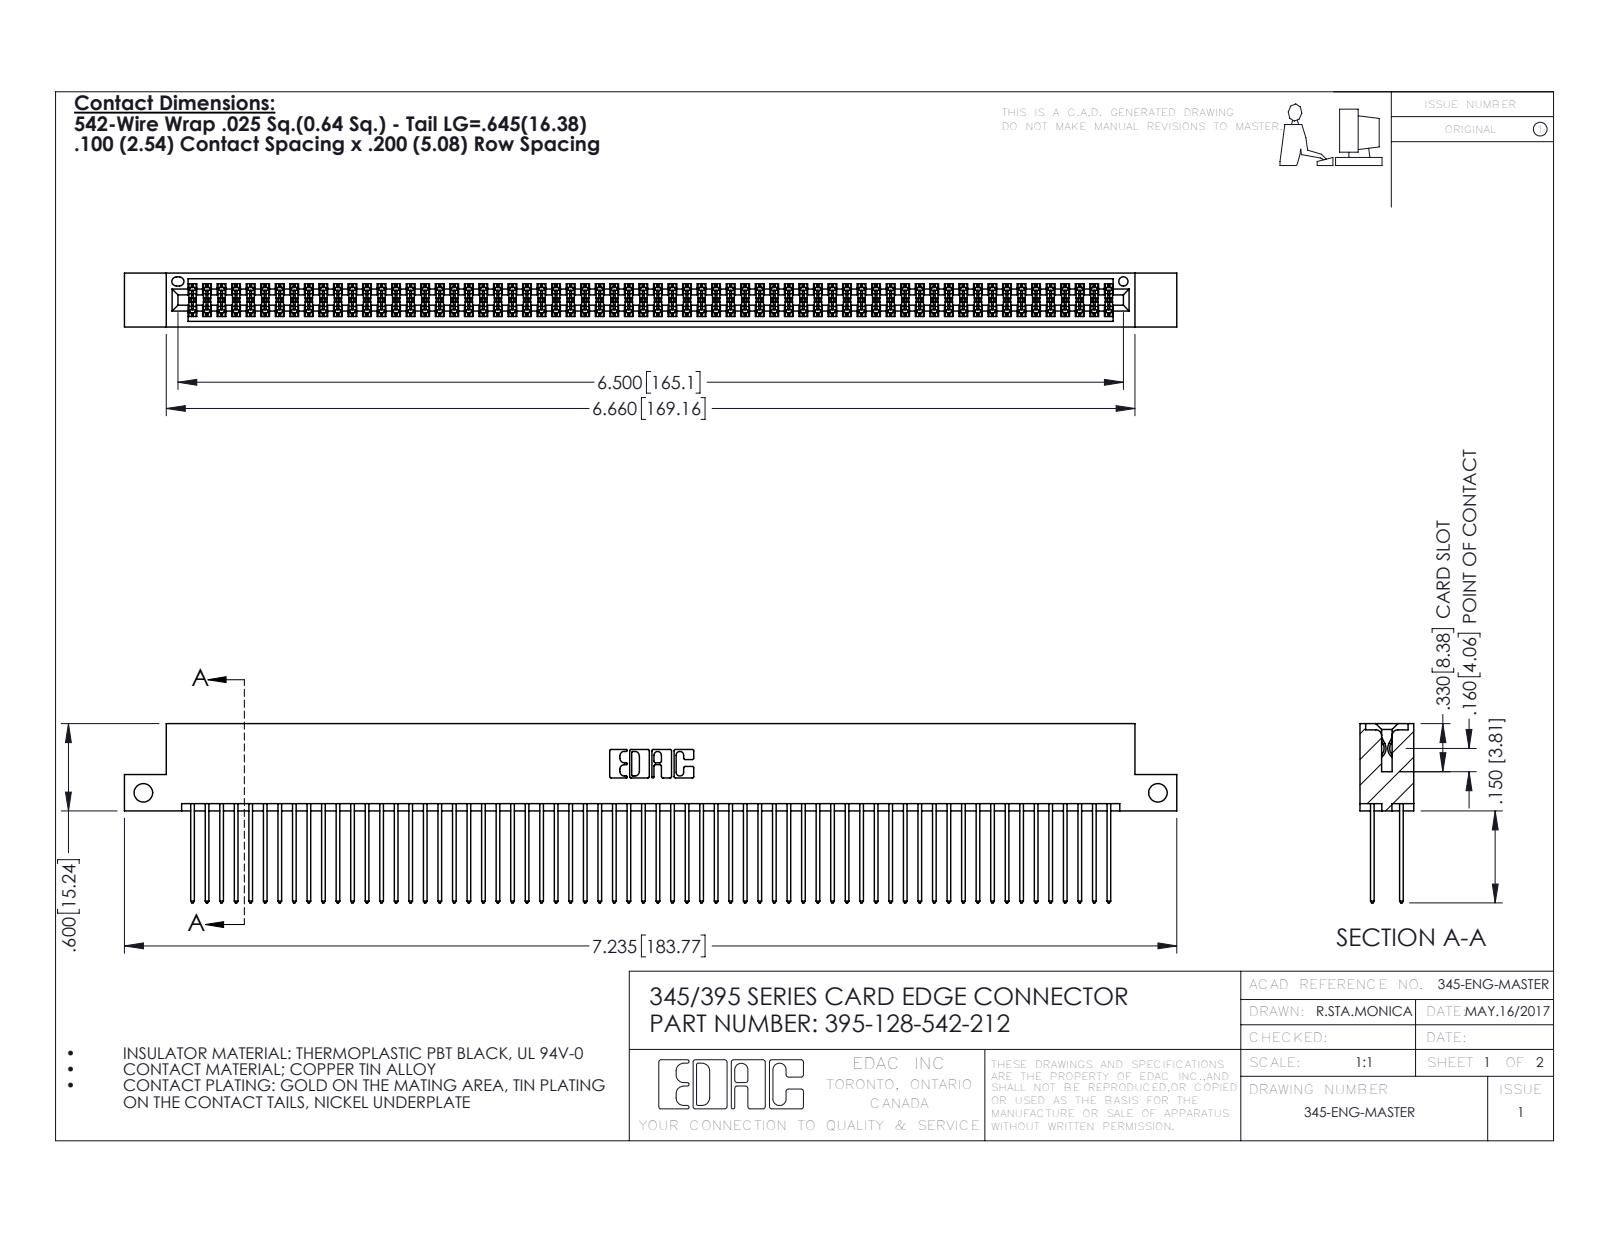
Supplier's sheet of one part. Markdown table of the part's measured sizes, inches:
| quantity | value |
| --- | --- |
| part name | 395-128-542-212; 345-292-001_345-293-142; 345 Part_Flush Mounting Lugs - Side Mount |
| STEP written by | SolidWorks 2016 (CONFIG_CONTROL_DESIGN) |
| units | inches |
| bodies | 129 solids, 6526 faces (4304 planar, 2222 cylindrical, 0 other) |
| overall size | 7.235 × 1.232 × 0.37 |
| volume | 1.133 in³ |
| surface area | 47.31 in² |
| round holes (diameter × count) | 0.128 × 2, 0.064 × 1 |
| partial cylindrical surfaces (radius × count) | 0.006 × 192, 0.01 × 128, 0.01 × 22, 0.007 × 6, 0.031 × 6, 0.026 × 3, 0.014 × 2, 0.019 × 2 |
| main face-to-face distances | 0.298, 0.072, 0.2, 0.098, 0.272, 0.025, 0.225, 0.37, 0.175, 0.149 |
| hole center spacings | 6.975 |
